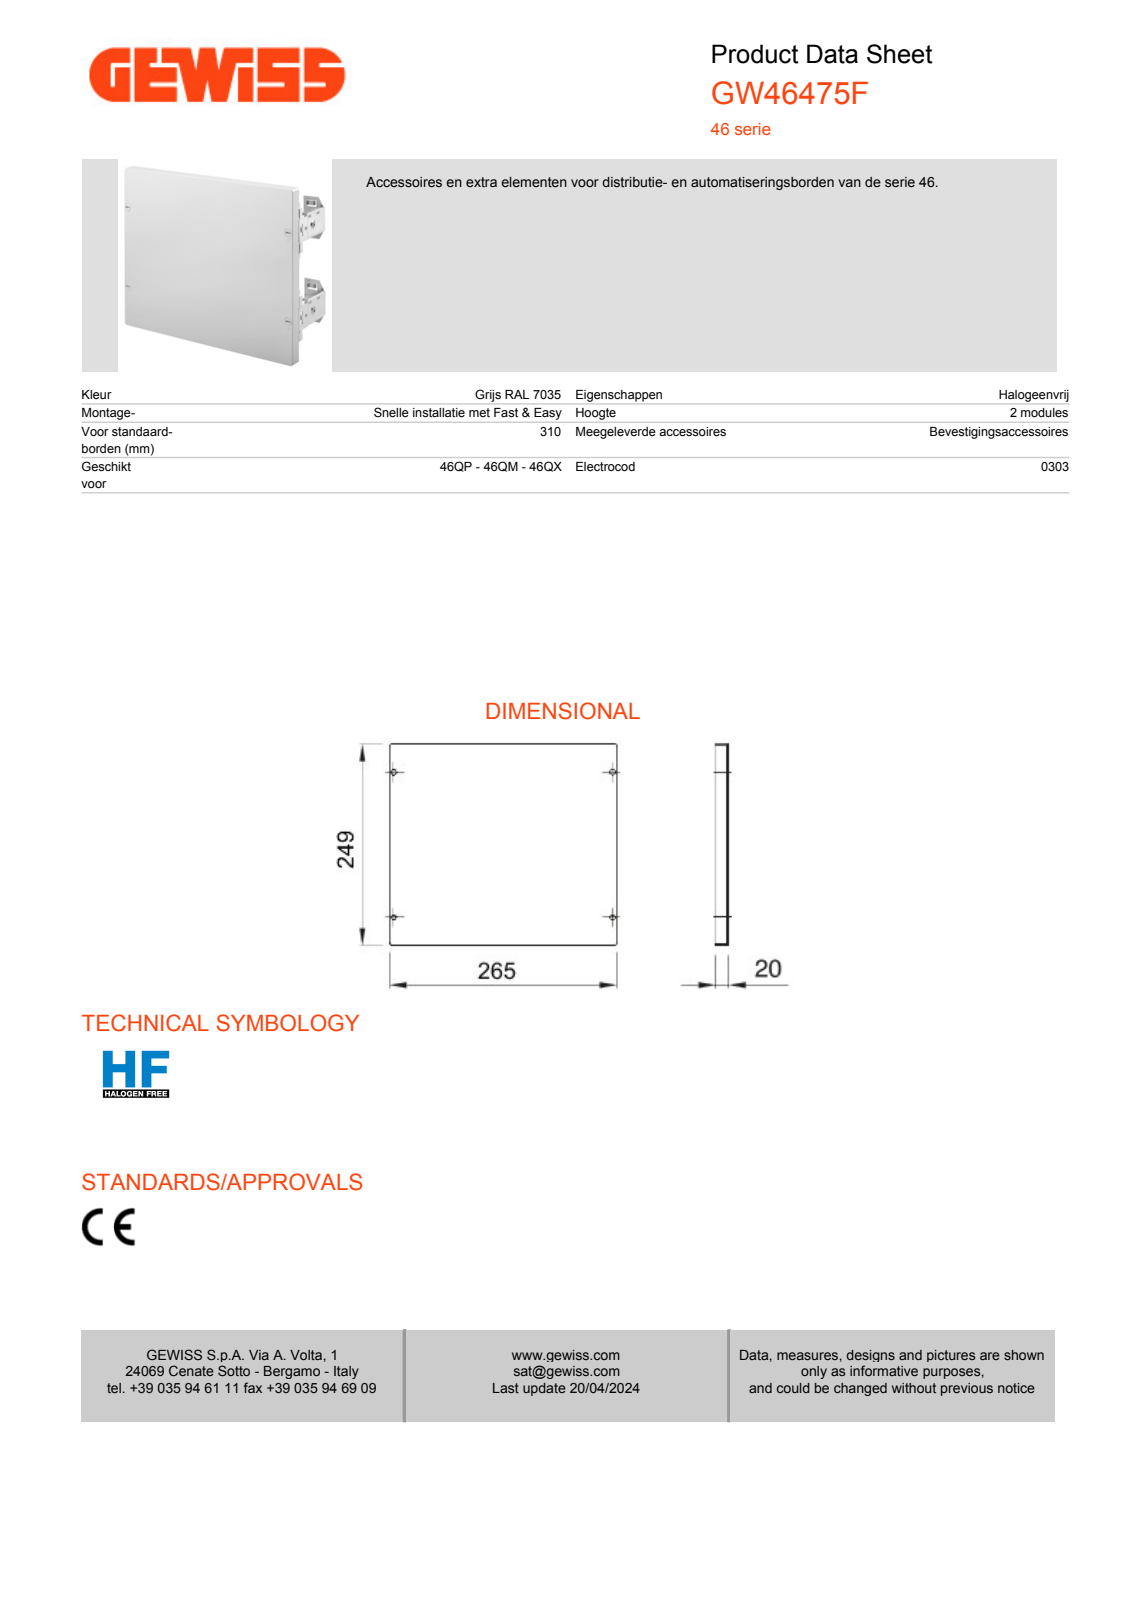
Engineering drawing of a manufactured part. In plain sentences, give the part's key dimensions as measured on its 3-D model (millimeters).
The part is named "55710990F2XX_MOSTRINA_CIECA_DOP; PARTBODY_2-52983; 55718969DXXX_STAFFA_SUPP__LG_68_ASM; GW46475F_ASM". Its 3-D file was written by "CREO PARAMETRIC BY PTC INC, 2020354 (CONFIG_CONTROL_DESIGN)". It is 5 solids with 1106 faces: 694 planar, 340 cylindrical and 72 other. Overall it measures 270 by 249 by 93.37 millimeters. Its volume is 305 916 cubic millimeters and its surface area 236 549 square millimeters. Round holes: 16 of diameter 1.2, 8 of diameter 4.5, 4 of diameter 4, 4 of diameter 6.5, 2 of diameter 8. Round bosses or shafts: 16 of diameter 3, 4 of diameter 14.4, 4 of diameter 13.4, 4 of diameter 9.6. Partial cylindrical surfaces (rounded edges, fillets, slot ends): 70 of radius 1.5, 16 of radius 1.15, 8 of radius 0.5, 8 of radius 4.5, 8 of radius 4.67, 4 of radius 0.9, 4 of radius 1.25, 4 of radius 3. The main face-to-face distances are 3, 1.5, 4, 264, 67, 20, 88.5, 17, 85.5, 68.5. The hole center spacings are 125, 23.57, 34.36, 37.42, 57.1, 200.85, 217.48, 221.72.
